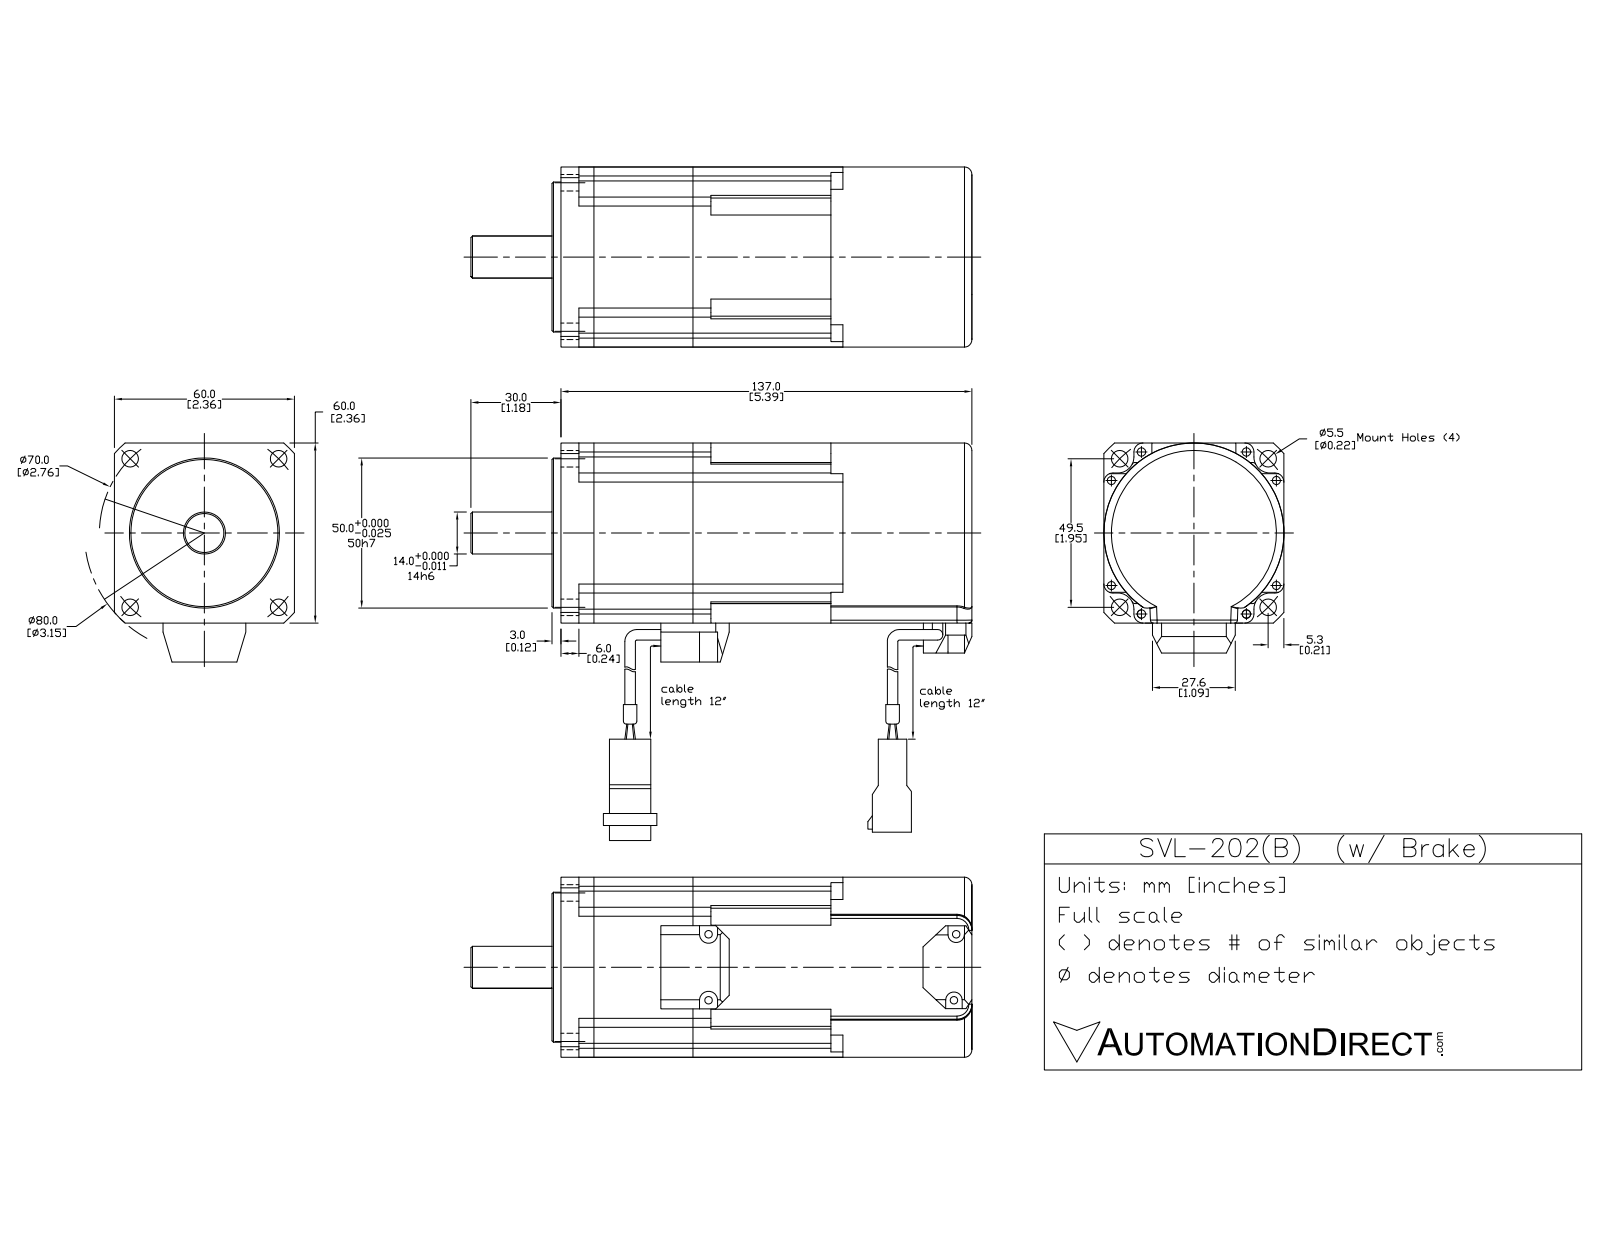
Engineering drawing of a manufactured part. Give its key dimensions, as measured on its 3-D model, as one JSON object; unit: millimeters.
{"part_name": "SVL-202B", "step_written_by": "SolidWorks 2015 (AUTOMOTIVE_DESIGN)", "units": "millimeters", "bodies": {"solids": 18, "faces": 417, "planar": 241, "cylindrical": 141, "other": 35}, "overall_size": [167, 73.4, 63.26], "volume_mm3": 443825, "surface_area_mm2": 63603, "round_holes": [[5.5, 4], [18.5, 1]], "round_bosses_or_shafts": [[5.5, 5], [5, 4], [3.5, 4], [60, 1], [50, 1], [14, 1], [7, 1]], "partial_cylinders_radius": [[1, 14], [3, 12], [2, 4], [2.5, 4], [2.75, 4], [5.3, 4], [40, 1]], "face_to_face_distances": [33, 60, 46, 79, 47, 93, 126, 44, 11, 0.5], "hole_center_spacings": [35, 49.5, 70]}
